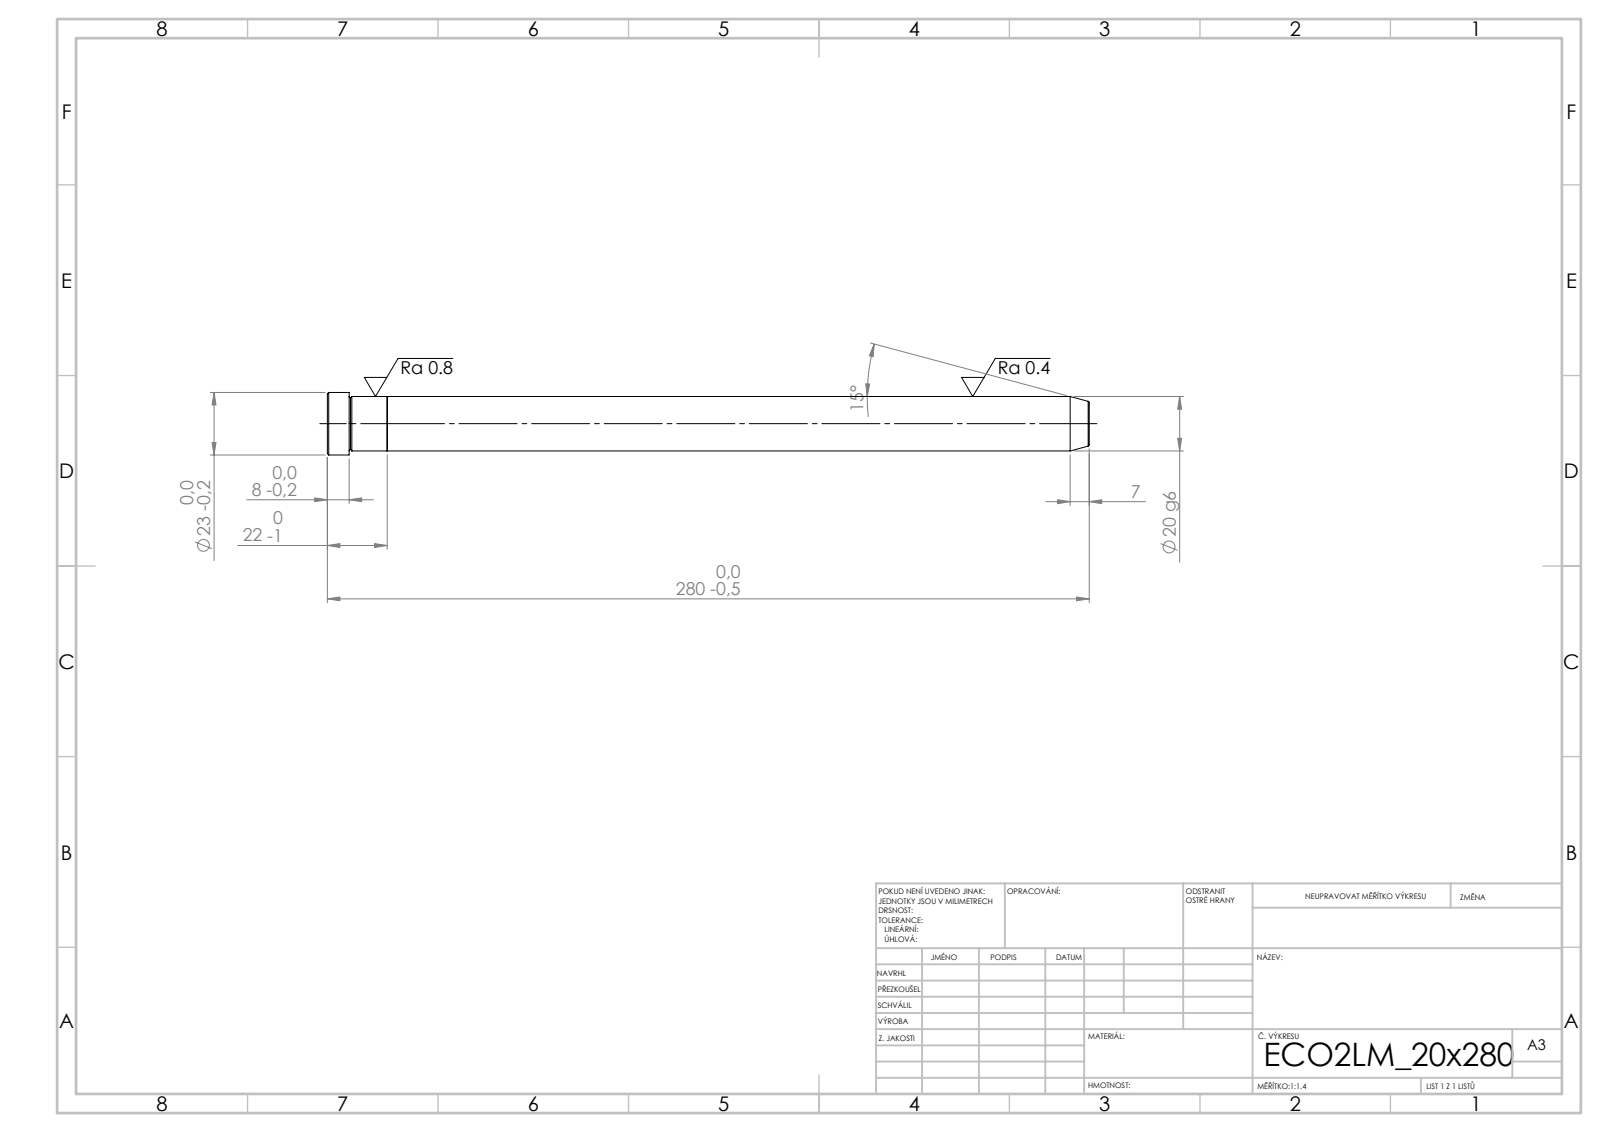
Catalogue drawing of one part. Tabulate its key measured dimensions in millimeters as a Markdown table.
| quantity | value |
| --- | --- |
| STEP written by | SolidWorks 2019 (CONFIG_CONTROL_DESIGN) |
| units | millimeters |
| bodies | 2 solids, 21 faces (5 planar, 6 cylindrical, 10 other) |
| overall size | 280 × 23 × 23 |
| volume | 88 354 mm³ |
| surface area | 18 999 mm² |
| round bosses / shafts (diameter × count) | 23 × 1, 20 × 1 |
| main face-to-face distances | 22, 258, 280, 272, 14, 8 |
